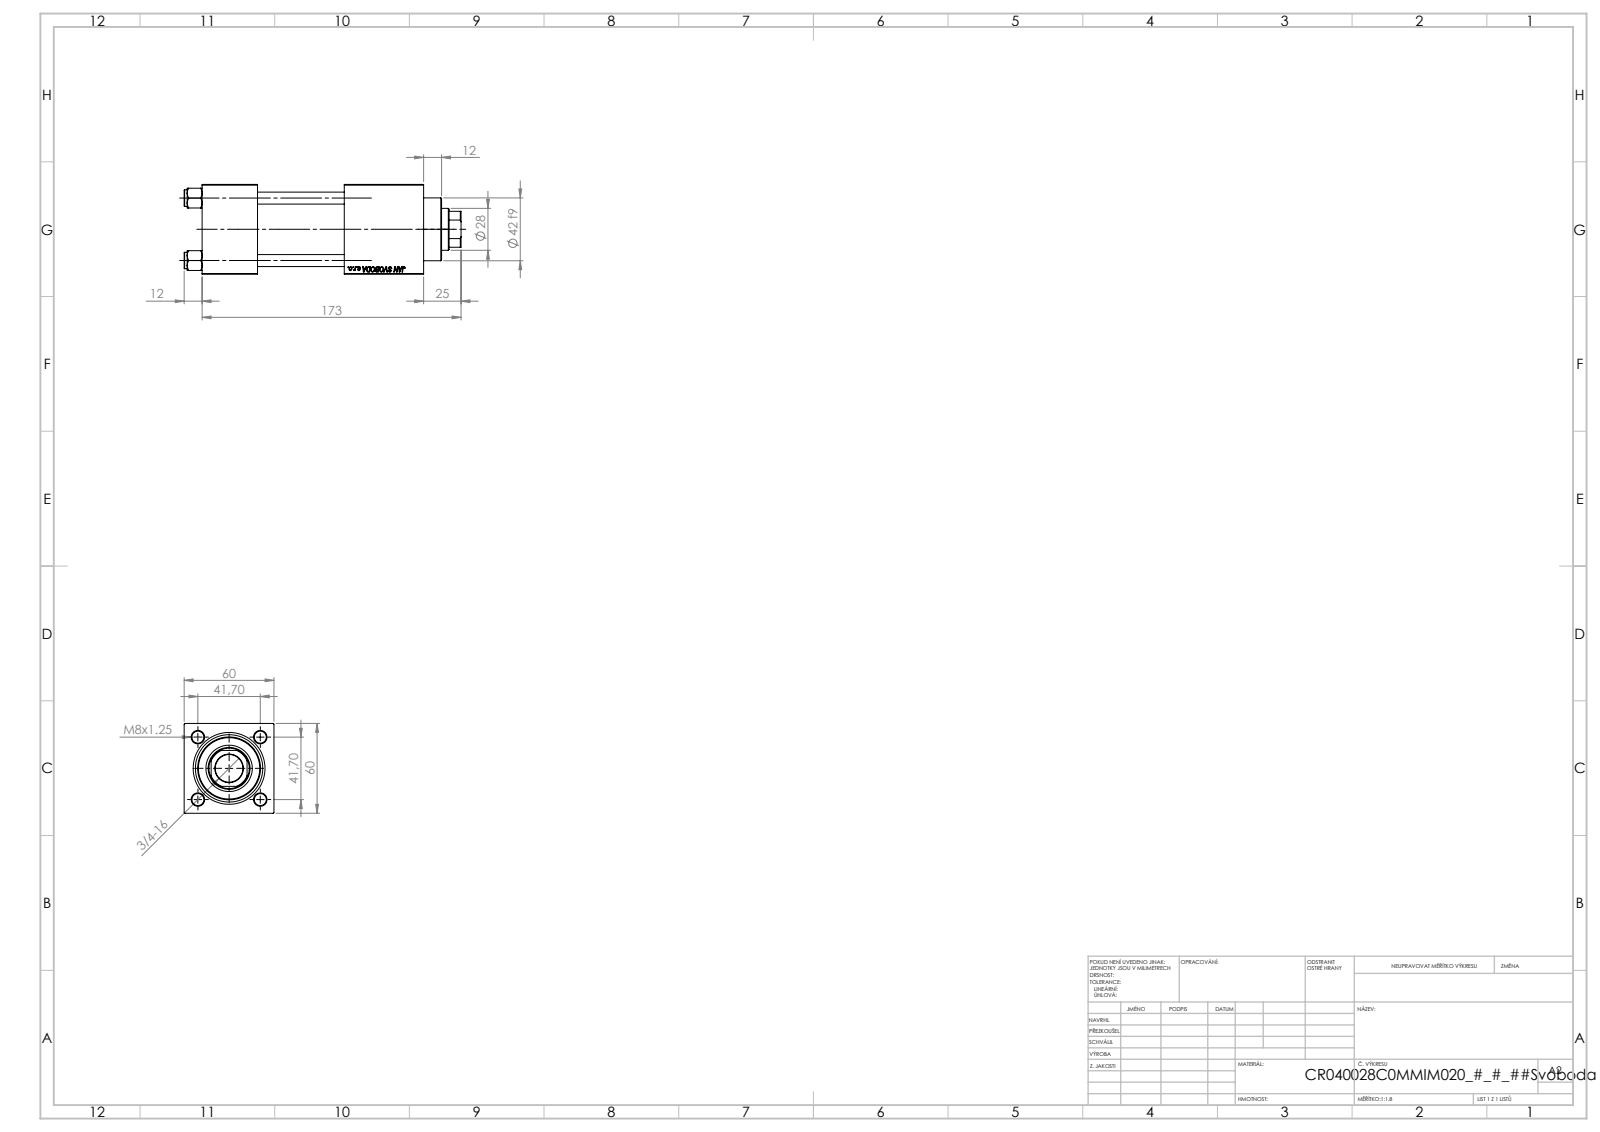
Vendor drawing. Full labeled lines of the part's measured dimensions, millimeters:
Part name (STEP PRODUCT): V215CR_VCP_C; V215_VC_A; V215CR_C_Body; V215CR_C_TYCINKA (+1 more)
STEP written by: SolidWorks 2019 (CONFIG_CONTROL_DESIGN)
Units: millimetres
Bodies: 11 solids, 1148 faces (526 planar, 86 cylindrical, 536 other)
Overall size (bounding box): 185 × 60 × 60
Volume: 424 489 mm³ · Surface area: 111 347 mm²
Round holes (diameter × count): ⌀8 ×4, ⌀7 ×2, ⌀16.66 ×2, ⌀24 ×2, ⌀18.5 ×1, ⌀28 ×1, ⌀31 ×1, ⌀40 ×1, ⌀45 ×1
Round bosses / shafts (diameter × count): ⌀11 ×4, ⌀46 ×1, ⌀42 ×1
Partial cylindrical surfaces — rounded edges, fillets, slot ends (radius × count): R13.5 ×1
Main face-to-face distances: 60, 37, 58, 95, 53, 119.3, 82.3, 24.3, 148, 111
Hole centre spacings: 29.49, 41.7, 58.97, 92.5
